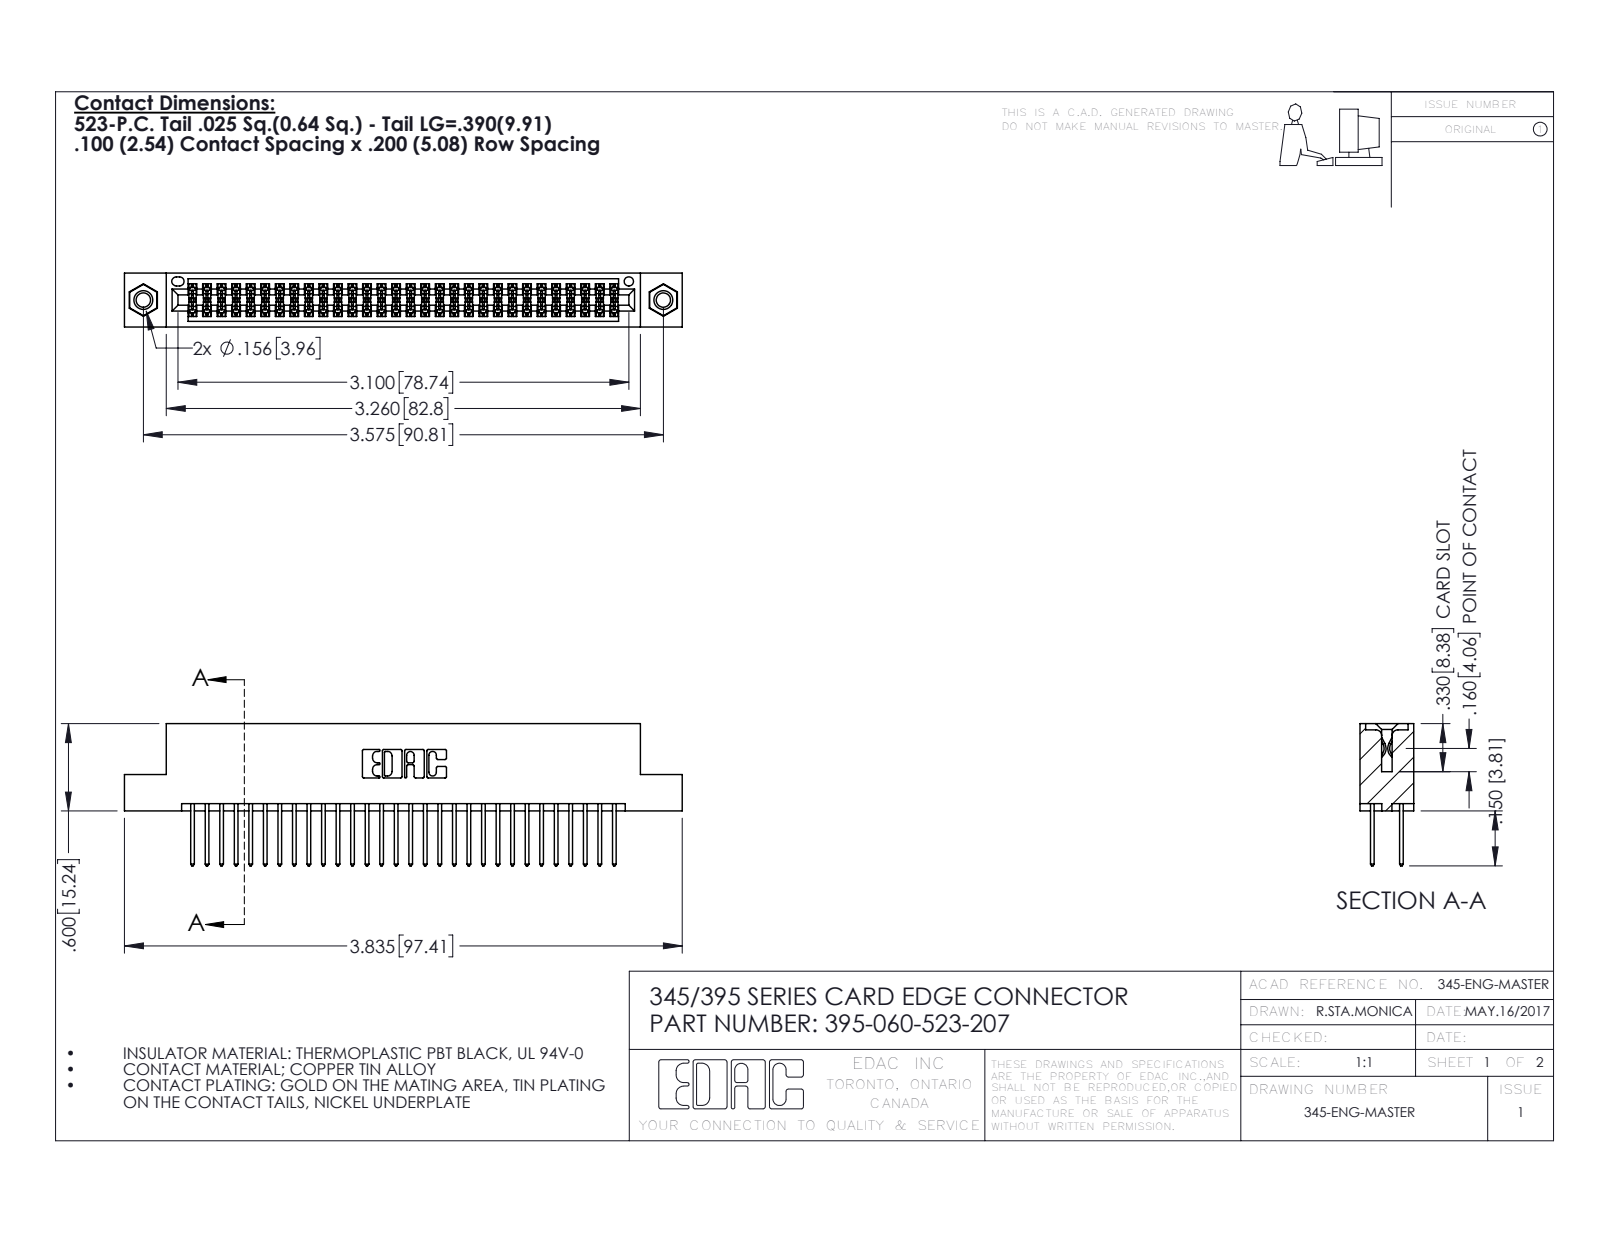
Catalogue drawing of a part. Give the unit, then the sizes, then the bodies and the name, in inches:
Units: inches
Overall size (bounding box): 3.835 × 0.977 × 0.37
Round holes (diameter × count): ⌀0.098 ×2, ⌀0.125 ×2, ⌀0.156 ×2, ⌀0.064 ×1
Round bosses / shafts (diameter × count): ⌀0.155 ×2
Partial cylindrical surfaces — rounded edges, fillets, slot ends (radius × count): R0.006 ×90, R0.01 ×60, R0.01 ×22, R0.007 ×6, R0.031 ×6, R0.026 ×3, R0.014 ×2, R0.019 ×2
Main face-to-face distances: 0.072, 0.298, 0.2, 0.098, 0.272, 0.025, 0.37, 0.225, 0.175, 0.149
Hole centre spacings: 0.27, 3.34, 3.575
Volume: 0.577 in³ · Surface area: 22.21 in²
Bodies: 63 solids, 3186 faces (2092 planar, 1078 cylindrical, 16 other)
Part name (STEP PRODUCT): 345 Part_Flush Mounting Lugs - 0.156 Dia-TI; 395-060-523-207; 345-250-001_345-250-005-103; 345-292-001_345-293-123
STEP written by: SolidWorks 2016 (CONFIG_CONTROL_DESIGN)
